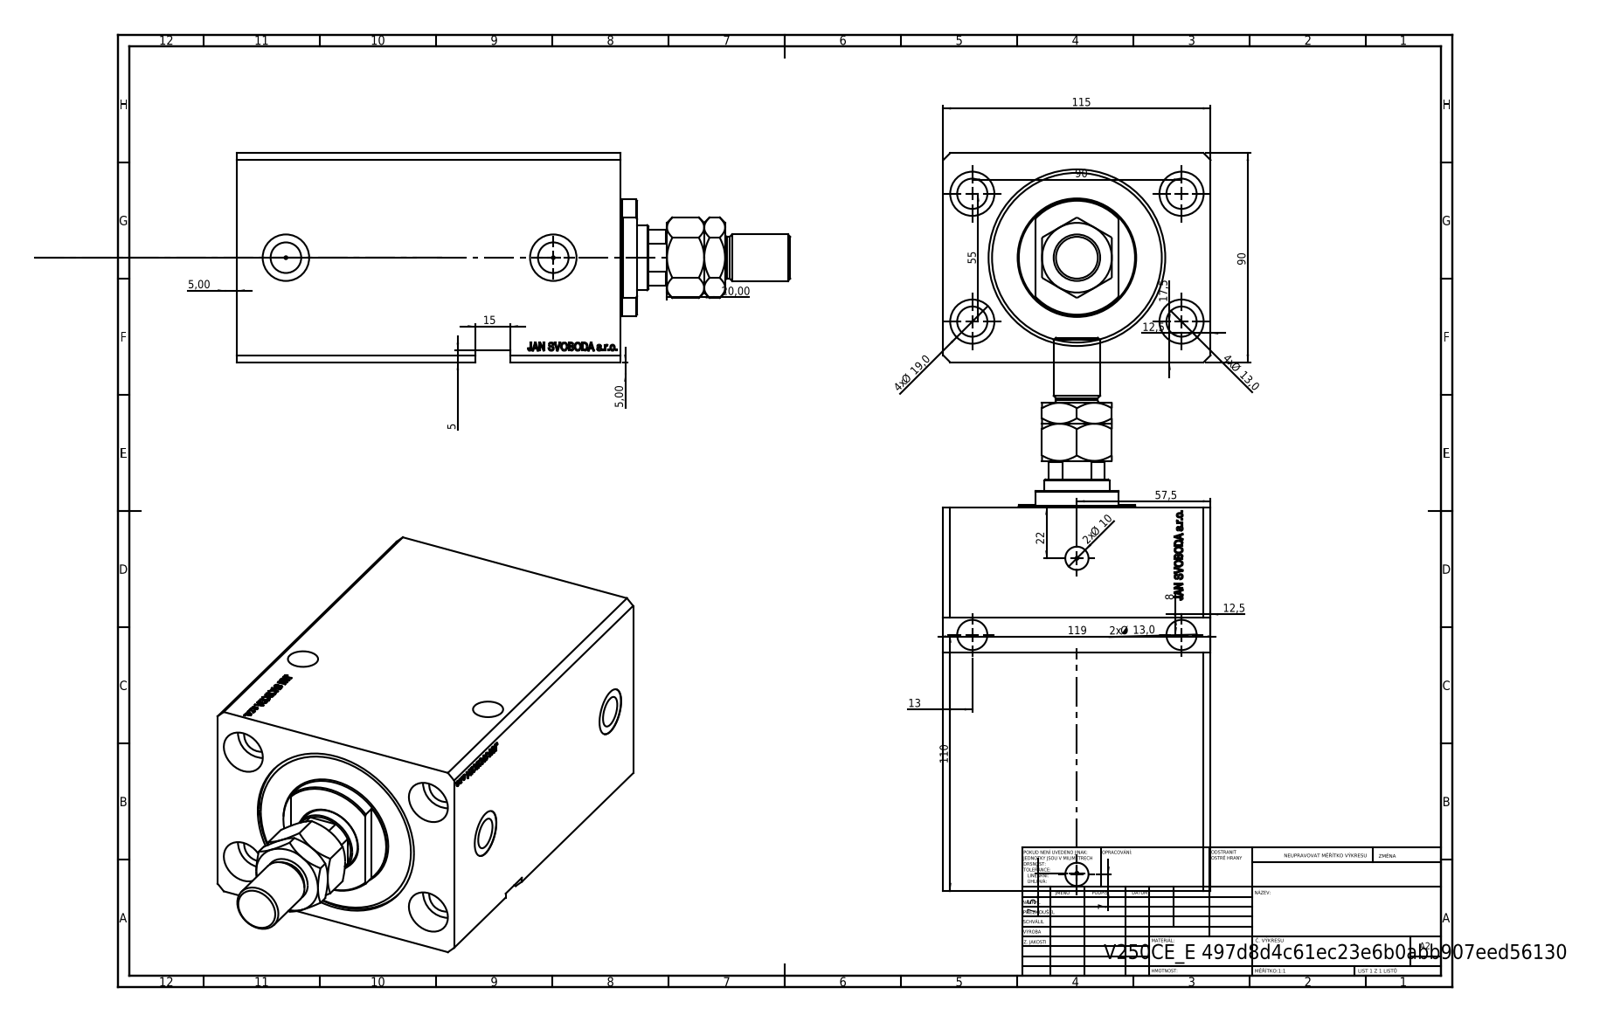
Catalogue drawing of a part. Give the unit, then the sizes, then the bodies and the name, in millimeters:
Units: millimetres
Overall size (bounding box): 237.9 × 115 × 90
Round holes (diameter × count): ⌀13 ×6, ⌀1.25 ×4, ⌀19 ×4, ⌀10 ×2, ⌀13.16 ×2, ⌀20 ×2, ⌀18.5 ×1, ⌀28 ×1, ⌀63 ×1, ⌀76 ×1
Round bosses / shafts (diameter × count): ⌀50 ×1, ⌀20 ×1, ⌀18 ×1
Partial cylindrical surfaces — rounded edges, fillets, slot ends (radius × count): R13.5 ×1
Main face-to-face distances: 90, 115, 165, 17.9, 147.1, 117, 134.9, 30.1, 54.9, 80
Hole centre spacings: 52.74, 90, 55, 55.8, 105.48, 111.92, 112.4, 0.53
Volume: 1 405 000 mm³ · Surface area: 204 891 mm²
Bodies: 4 solids, 1002 faces (486 planar, 100 cylindrical, 416 other)
Part name (STEP PRODUCT): V250CE_E_Body; MTA; V250CE_VC_E; V250CE_C_VCP
STEP written by: SolidWorks 2019 (CONFIG_CONTROL_DESIGN)
